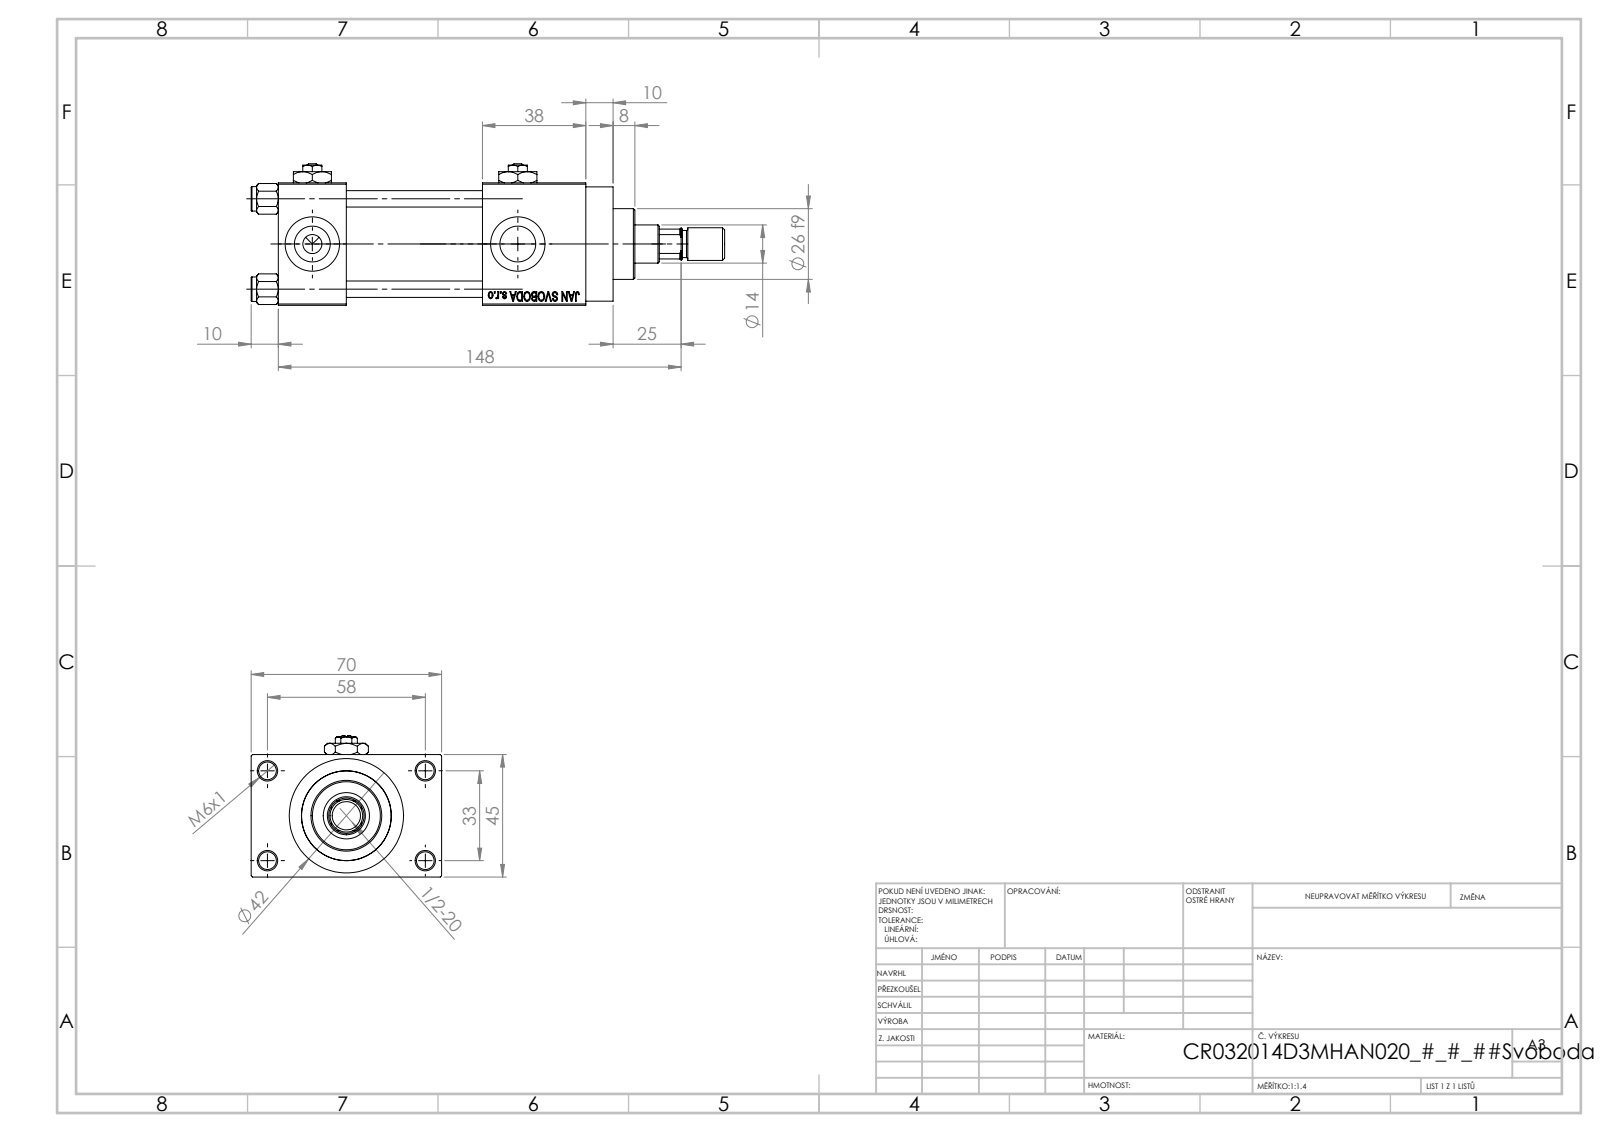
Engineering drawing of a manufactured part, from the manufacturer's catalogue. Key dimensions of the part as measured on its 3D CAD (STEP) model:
Part name (STEP PRODUCT): ROD_END_AH; V215CR_VCP_D; Zatka_pro_OIL_PORT; V215_VC_A (+3 more)
STEP written by: SolidWorks 2019 (CONFIG_CONTROL_DESIGN)
Units: millimetres
Bodies: 14 solids, 1215 faces (546 planar, 103 cylindrical, 566 other)
Overall size (bounding box): 174 × 70 × 52
Volume: 230 802 mm³ · Surface area: 77 978 mm²
Round holes (diameter × count): ⌀6.5 ×5, ⌀6 ×4, ⌀13.16 ×4, ⌀20 ×4, ⌀7 ×3, ⌀14 ×1, ⌀17 ×1, ⌀24 ×1, ⌀32 ×1, ⌀33 ×1
Round bosses / shafts (diameter × count): ⌀9 ×4, ⌀42 ×1, ⌀38 ×1, ⌀26 ×1, ⌀12 ×1, ⌀10 ×1
Partial cylindrical surfaces — rounded edges, fillets, slot ends (radius × count): R6.5 ×1
Main face-to-face distances: 45, 25, 50, 12.5, 75, 57.5, 88, 38, 113, 70
Hole centre spacings: 12.4, 23.48, 33.2, 33.37, 35.35, 45.6, 56.35, 33
